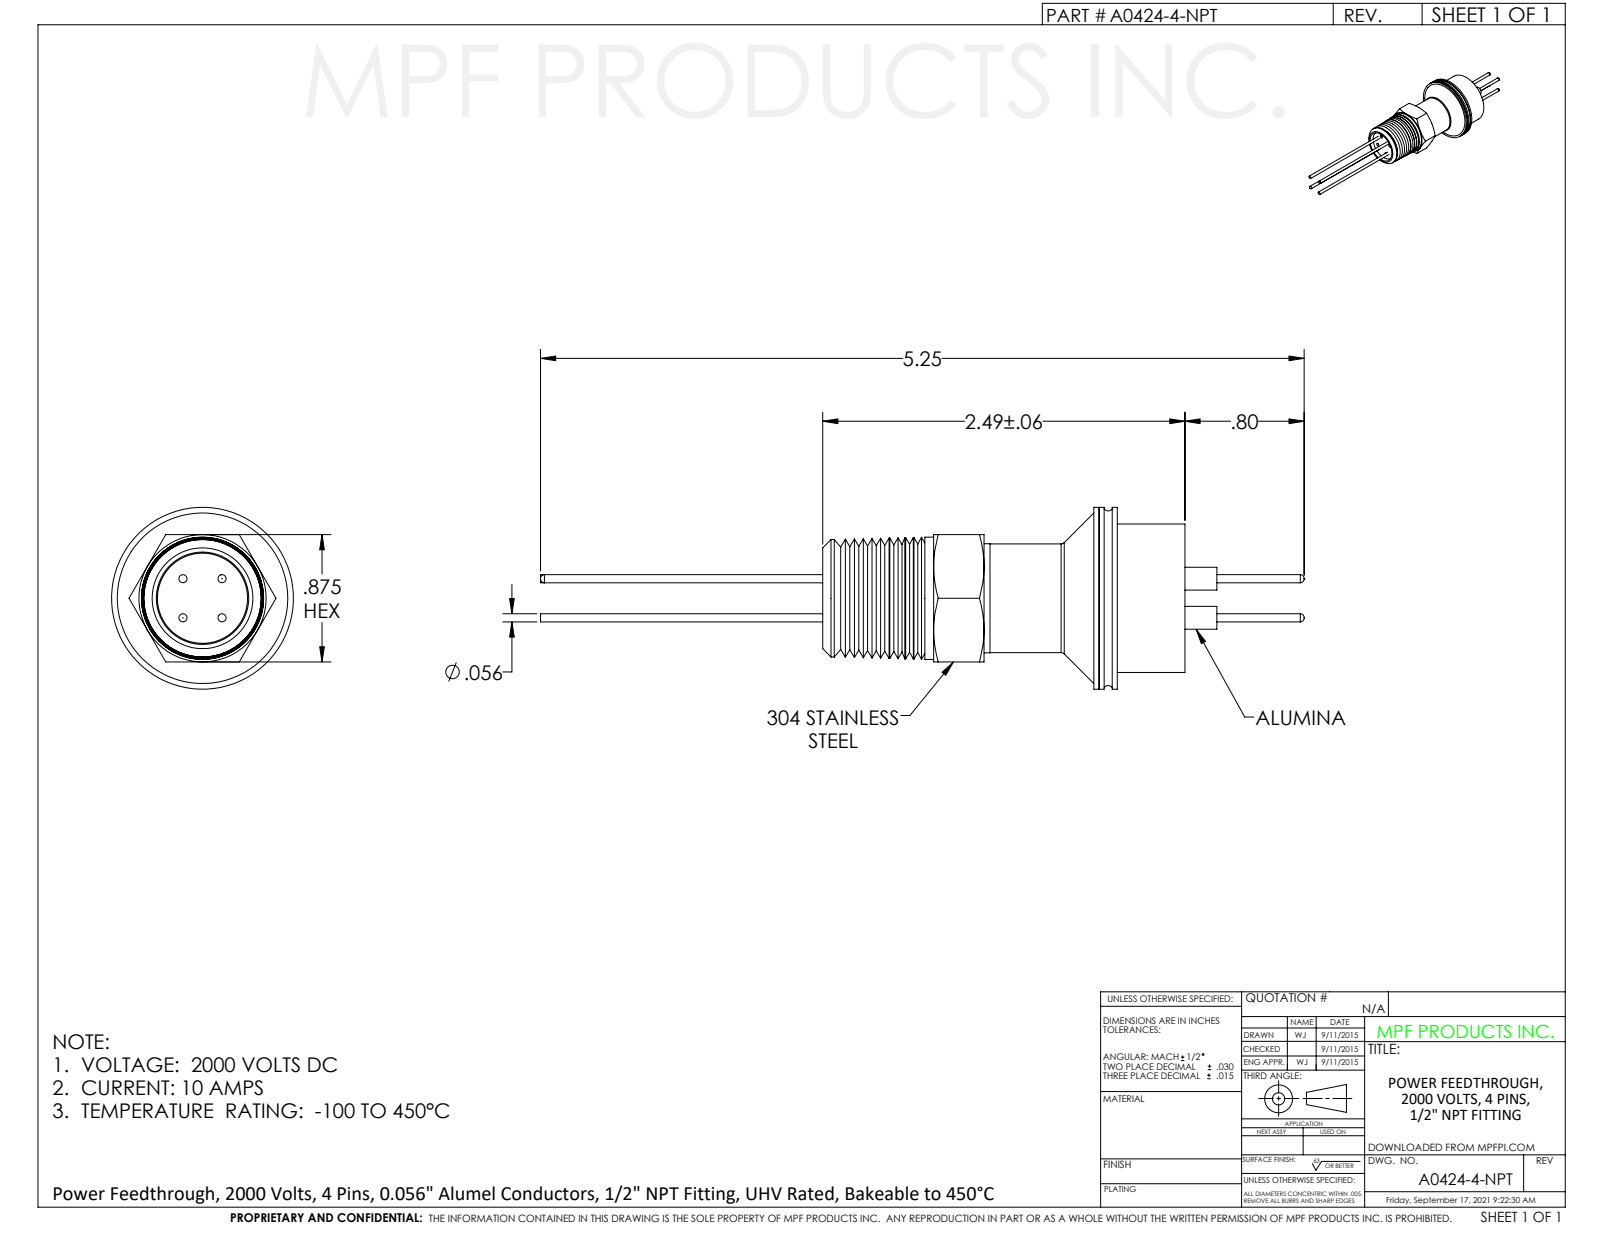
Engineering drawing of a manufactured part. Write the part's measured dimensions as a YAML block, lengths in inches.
part_name: "A0424-4-NPT"
step_written_by: "SolidWorks 2012 (CONFIG_CONTROL_DESIGN)"
units: inches
bodies: {solids: 1, faces: 258, planar: 51, cylindrical: 94, other: 113}
overall_size: [5.25, 1.25, 1.25]
volume: 0.602
surface_area: 24.05
round_holes:
  - {diameter: 0.159, count: 4}
  - {diameter: 0.625, count: 1}
  - {diameter: 0.675, count: 1}
  - {diameter: 0.94, count: 1}
  - {diameter: 0.96, count: 1}
  - {diameter: 0.97, count: 1}
round_bosses_or_shafts:
  - {diameter: 0.187, count: 4}
  - {diameter: 0.171, count: 4}
  - {diameter: 0.056, count: 4}
  - {diameter: 1.25, count: 1}
  - {diameter: 1.02, count: 1}
  - {diameter: 0.957, count: 1}
  - {diameter: 0.84, count: 1}
  - {diameter: 0.75, count: 1}
face_to_face_distances: [0.05, 0.875, 0.43, 0.38, 0.04, 2.382, 0.125, 0.555, 2.432, 2.472]
hole_center_spacings: [0.19, 0.269, 0.38]
